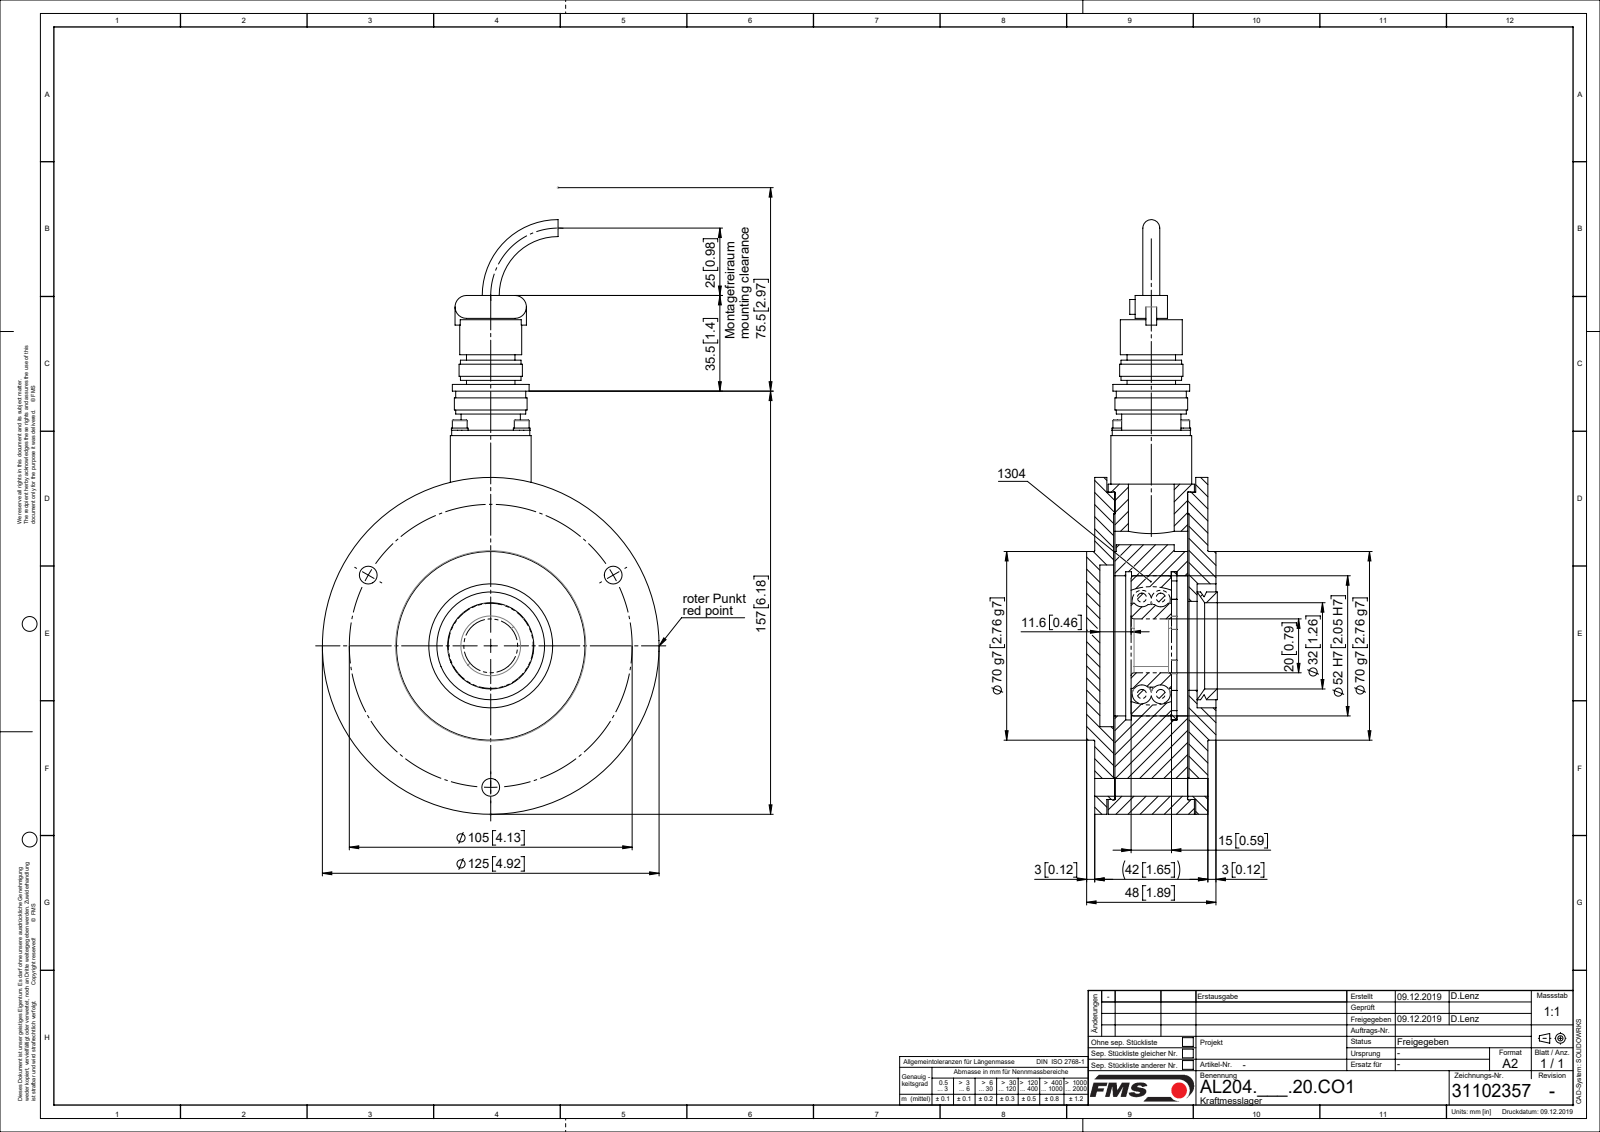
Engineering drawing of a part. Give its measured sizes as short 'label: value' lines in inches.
name: Federringe_DIN127A_M03; 130124.5_stp_01; 130419.2_01; PKL_1304_01 (+7 more)
written by: SolidWorks 2018 (CONFIG_CONTROL_DESIGN)
unit: in
bodies: 41 solids, 451 faces (124 planar, 207 cylindrical, 120 other)
size: 8.687 × 4.921 × 1.909
volume: 29.49 in³; area: 212.3 in²
holes: 10× ⌀0.26, 6× ⌀0.098, 4× ⌀0.122, 4× ⌀0.134, 1× ⌀0.157, 1× ⌀0.669, 1× ⌀0.787, 1× ⌀0.906, 1× ⌀1.26, 1× ⌀1.299, 1× ⌀1.811, 1× ⌀2.047
bosses: 6× ⌀0.217, 4× ⌀0.244, 4× ⌀0.118, 4× ⌀0.098, 1× ⌀4.921, 1× ⌀2.756, 1× ⌀2.047, 1× ⌀1.575
rounds: 4× R0.004, 2× R0.167, 2× R0.167, 1× R0.819, 1× R0.949
face distances: 0.295, 0.02, 1.358, 0.276, 1.378, 1.083, 0.118, 1.476, 1.063, 1.181
hole spacings: 2.067, 0.55, 0.64, 0.906, 1.518, 1.87, 2.402, 2.645
